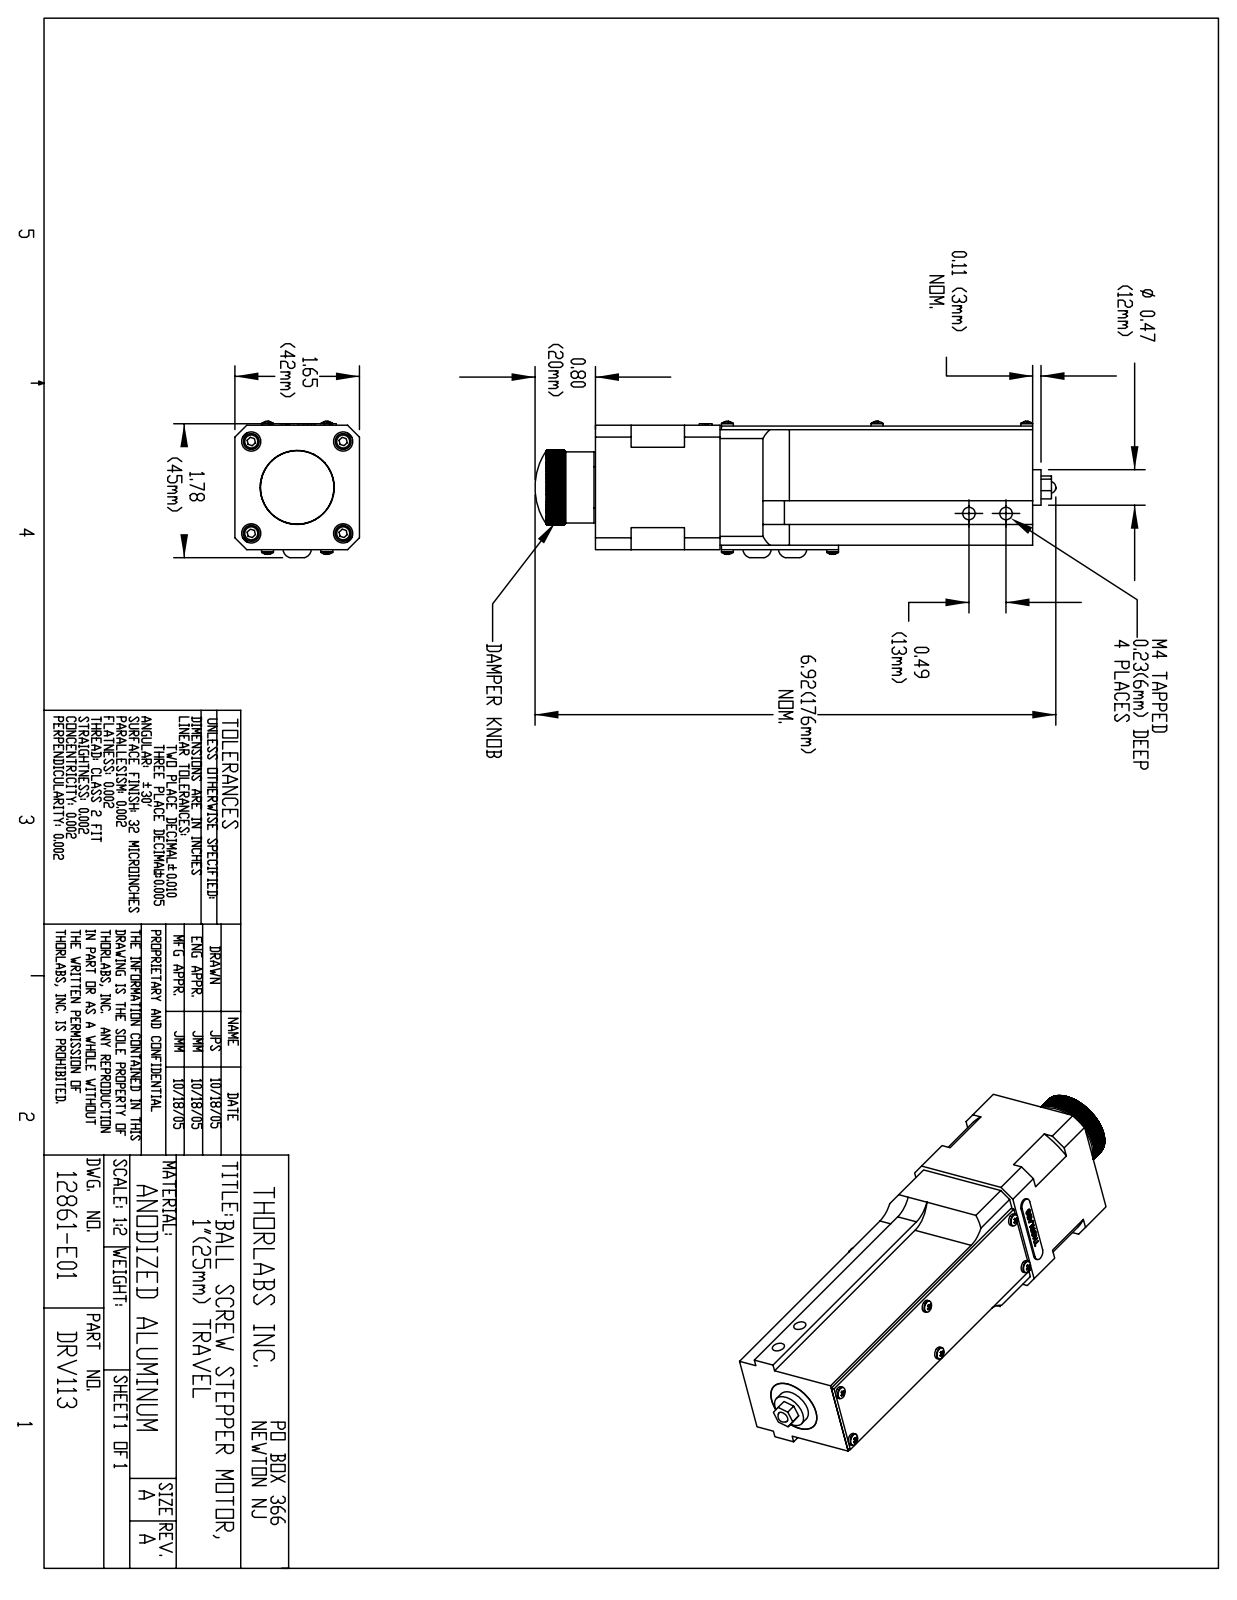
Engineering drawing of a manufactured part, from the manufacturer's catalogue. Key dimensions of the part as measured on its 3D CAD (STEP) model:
Part name (STEP PRODUCT): 12861-E0W
STEP written by: SolidWorks 2007 (AUTOMOTIVE_DESIGN)
Units: inches
Bodies: 0 solids, 1057 faces (738 planar, 241 cylindrical, 78 other)
Overall size (bounding box): 6.917 × 1.81 × 1.654
Round holes (diameter × count): ⌀0.256 ×4, ⌀0.165 ×2, ⌀0.189 ×2, ⌀0.098 ×1, ⌀0.157 ×1, ⌀0.748 ×1
Round bosses / shafts (diameter × count): ⌀0.157 ×8, ⌀0.213 ×4, ⌀0.945 ×1, ⌀0.472 ×1
Partial cylindrical surfaces — rounded edges, fillets, slot ends (radius × count): R0.394 ×4, R0.087 ×2, R0.492 ×1, R0.984 ×1
Main face-to-face distances: 0.059, 1.654, 1.594, 0.276, 1.378, 1.102, 1.583, 1.642, 1.535, 1.319
Hole centre spacings: 0.863, 1.22, 1.726, 0.472, 0.492
